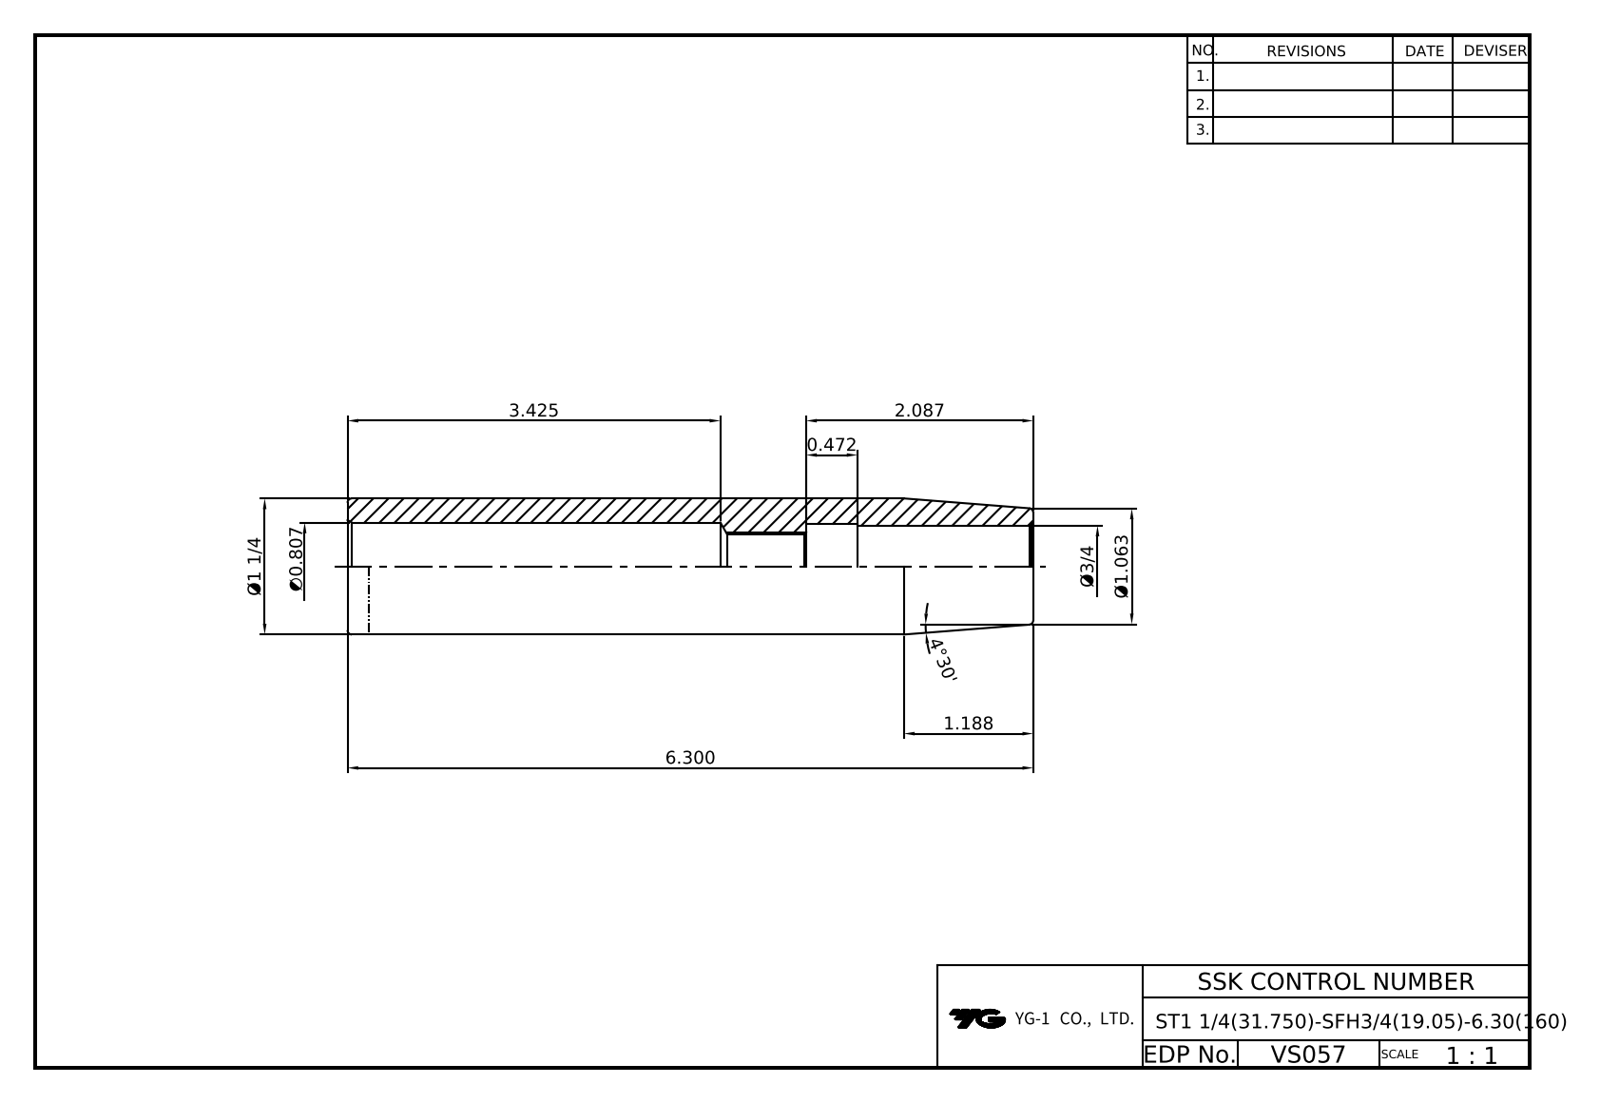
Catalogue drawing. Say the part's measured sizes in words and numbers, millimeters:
The part is named "ST31_75-SFH19_05-160". Its 3-D file was written by "CREO PARAMETRIC BY PTC INC, 2018500 (CONFIG_CONTROL_DESIGN)". It is 1 solid with 32 faces: 4 planar, 10 cylindrical and 18 other. Overall it measures 160 by 31.75 by 31.75 millimeters. Its volume is 75 070 cubic millimeters and its surface area 26 372 square millimeters. Round holes: 1 of diameter 16, 1 of diameter 19.05, 1 of diameter 19.65, 1 of diameter 20.5. Round bosses or shafts: 1 of diameter 31.75. The main face-to-face distances are 160, 107, 53, 119, 12, 41.
